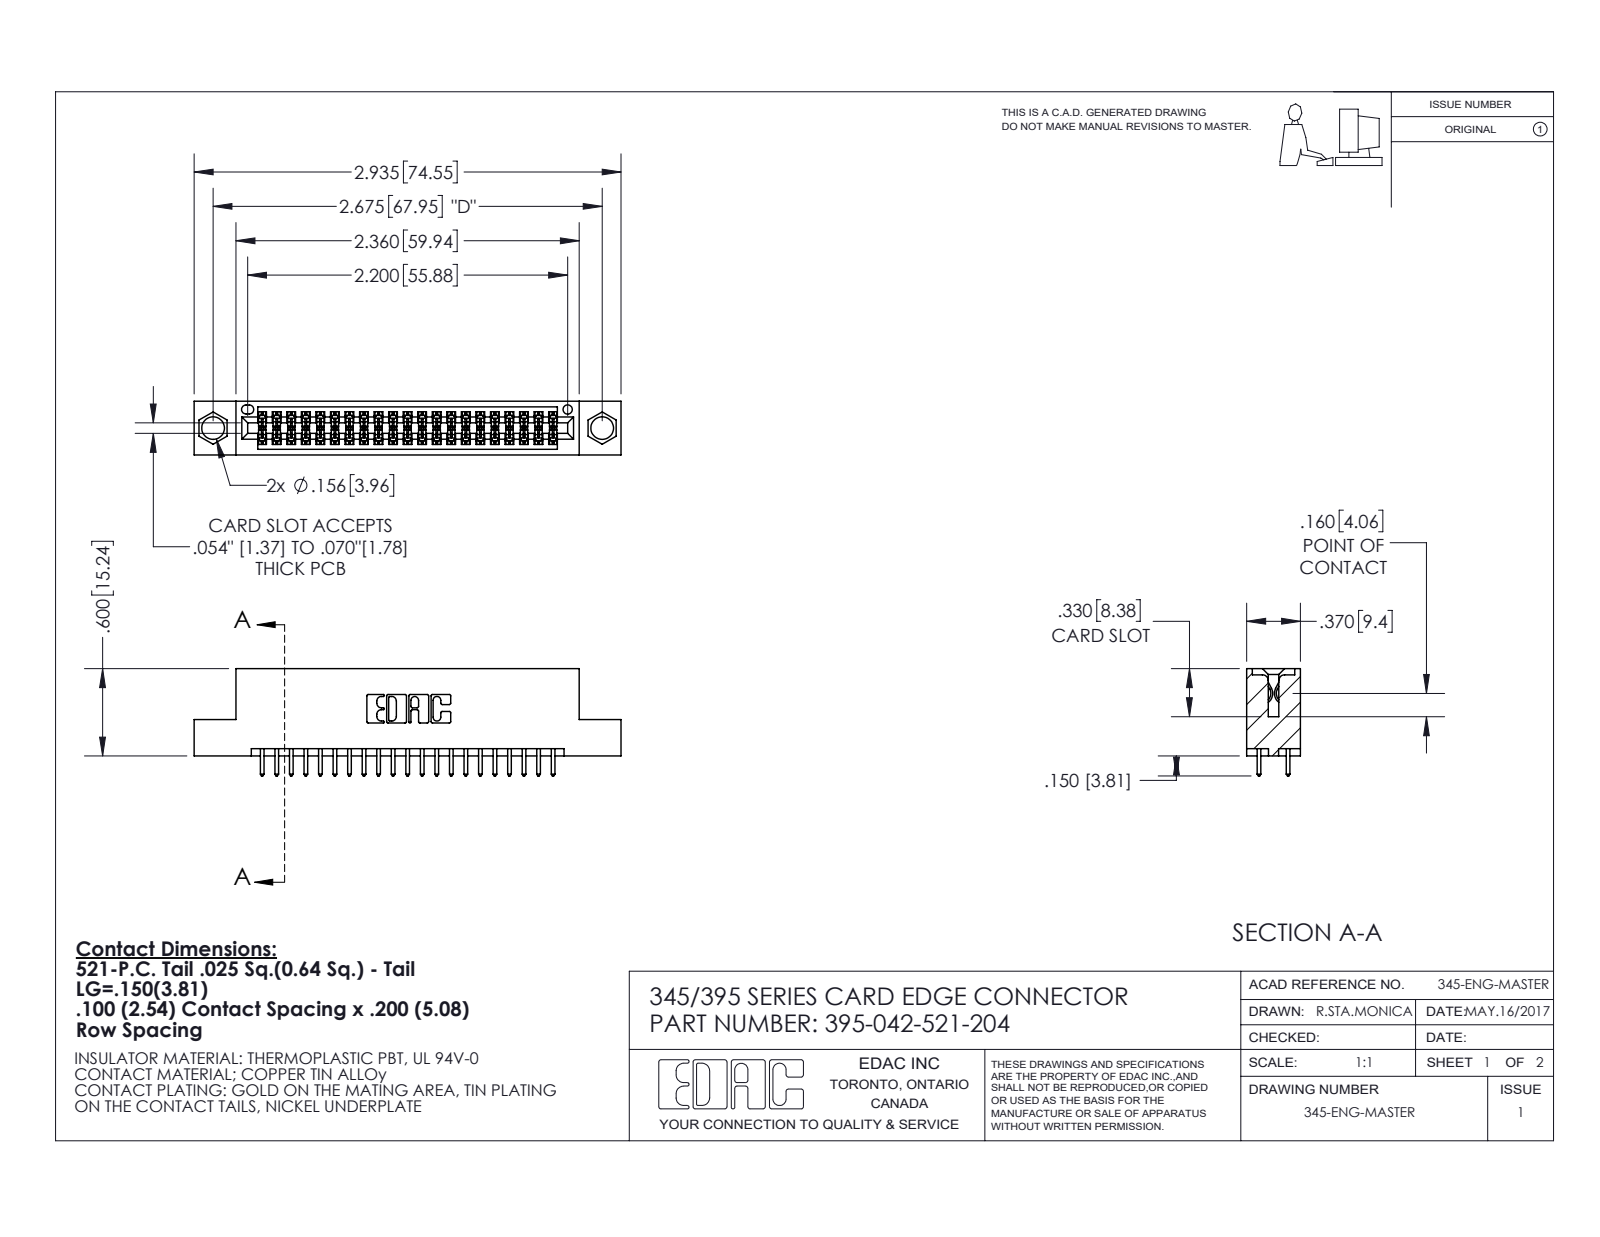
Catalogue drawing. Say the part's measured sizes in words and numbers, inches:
The part is named "345 Part_Flush Mounting Lugs - 0.156 Dia-TI; 345-292-001_345-293-121; 395-042-521-204". Its 3-D file was written by "SolidWorks 2020 (CONFIG_CONTROL_DESIGN)". It is 43 solids with 2240 faces: 1480 planar, 760 cylindrical and 0 other. Overall it measures 2.935 by 0.737 by 0.37 inches. Its volume is 0.423 cubic inches and its surface area 14.83 square inches. Round holes: 2 of diameter 0.156, 1 of diameter 0.064. Partial cylindrical surfaces (rounded edges, fillets, slot ends): 63 of radius 0.006, 42 of radius 0.01, 22 of radius 0.01, 6 of radius 0.007, 6 of radius 0.031, 3 of radius 0.026, 2 of radius 0.014, 2 of radius 0.019. The main face-to-face distances are 0.298, 0.072, 0.2, 0.37, 0.098, 0.272, 0.025, 0.225, 0.175, 0.149. The hole center spacings are 0.27, 2.441, 2.675.
